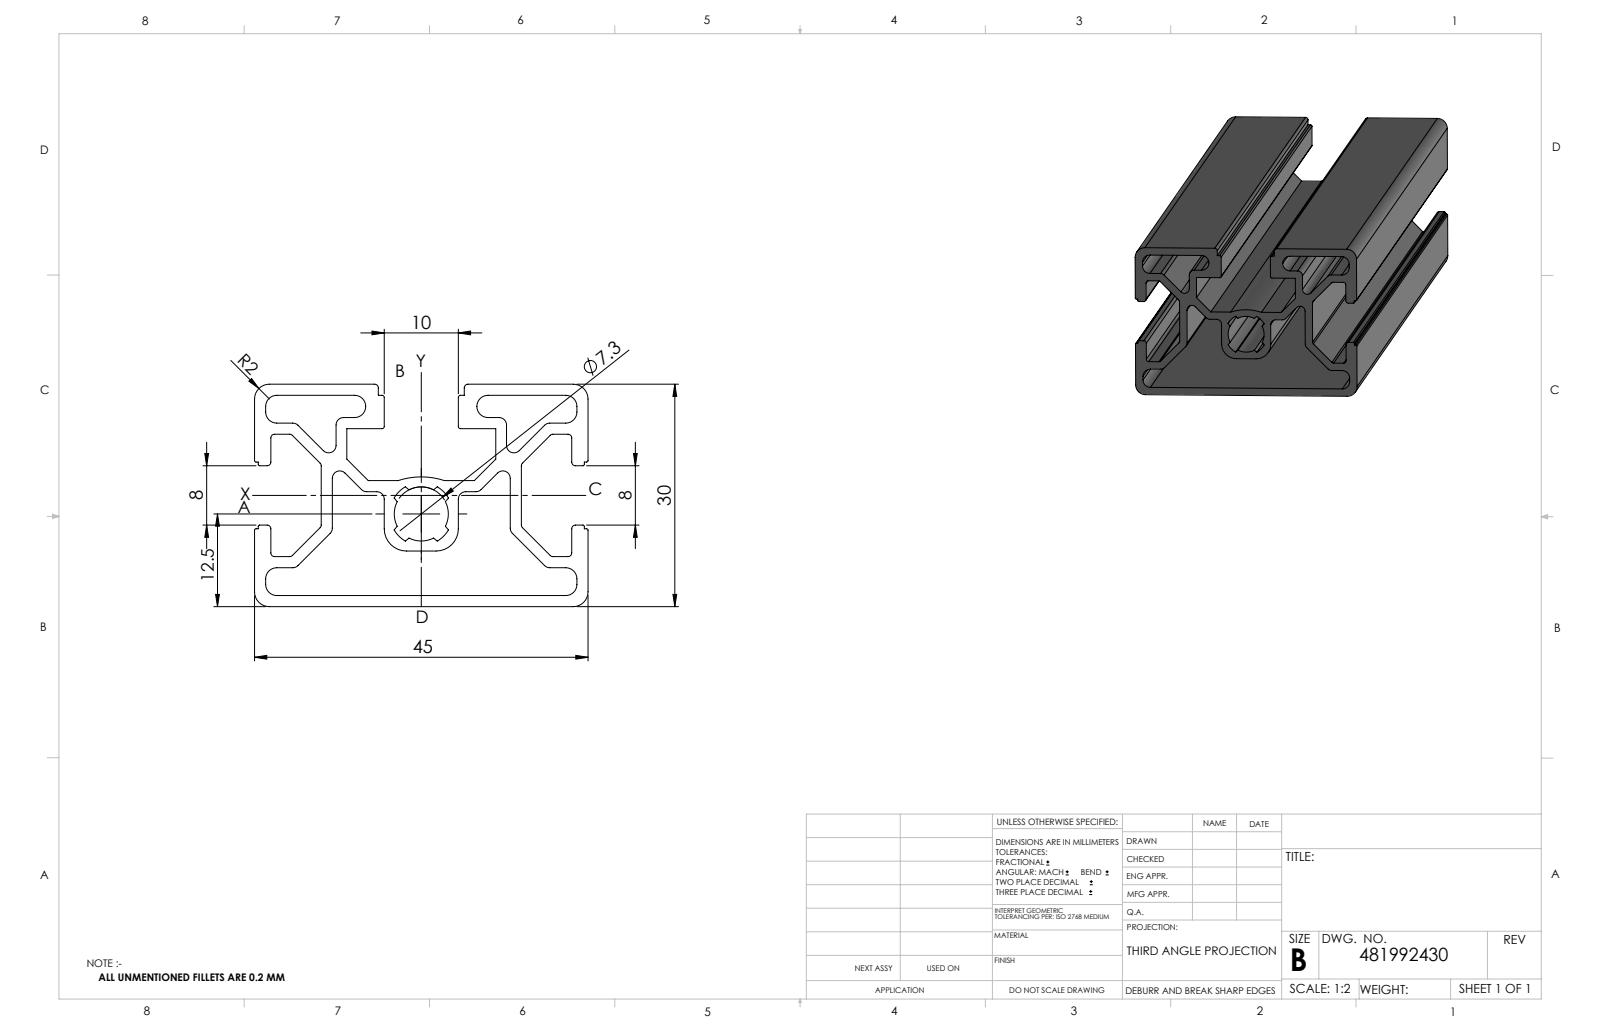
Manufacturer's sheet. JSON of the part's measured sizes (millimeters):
{"part_name": "481992430_c_1", "step_written_by": "SolidWorks 2014 (CONFIG_CONTROL_DESIGN)", "units": "millimeters", "bodies": {"solids": 1, "faces": 162, "planar": 85, "cylindrical": 77, "other": 0}, "overall_size": [200, 45, 30], "volume_mm3": 79019, "surface_area_mm2": 94856, "partial_cylinders_radius": [[0.5, 18], [1, 16], [1.5, 10], [0.2, 8], [0.3, 4], [2, 4], [3, 2], [3.65, 1]], "face_to_face_distances": [1.5, 28.5, 27, 30, 8.5, 17, 7, 9, 11.66, 17.5]}
